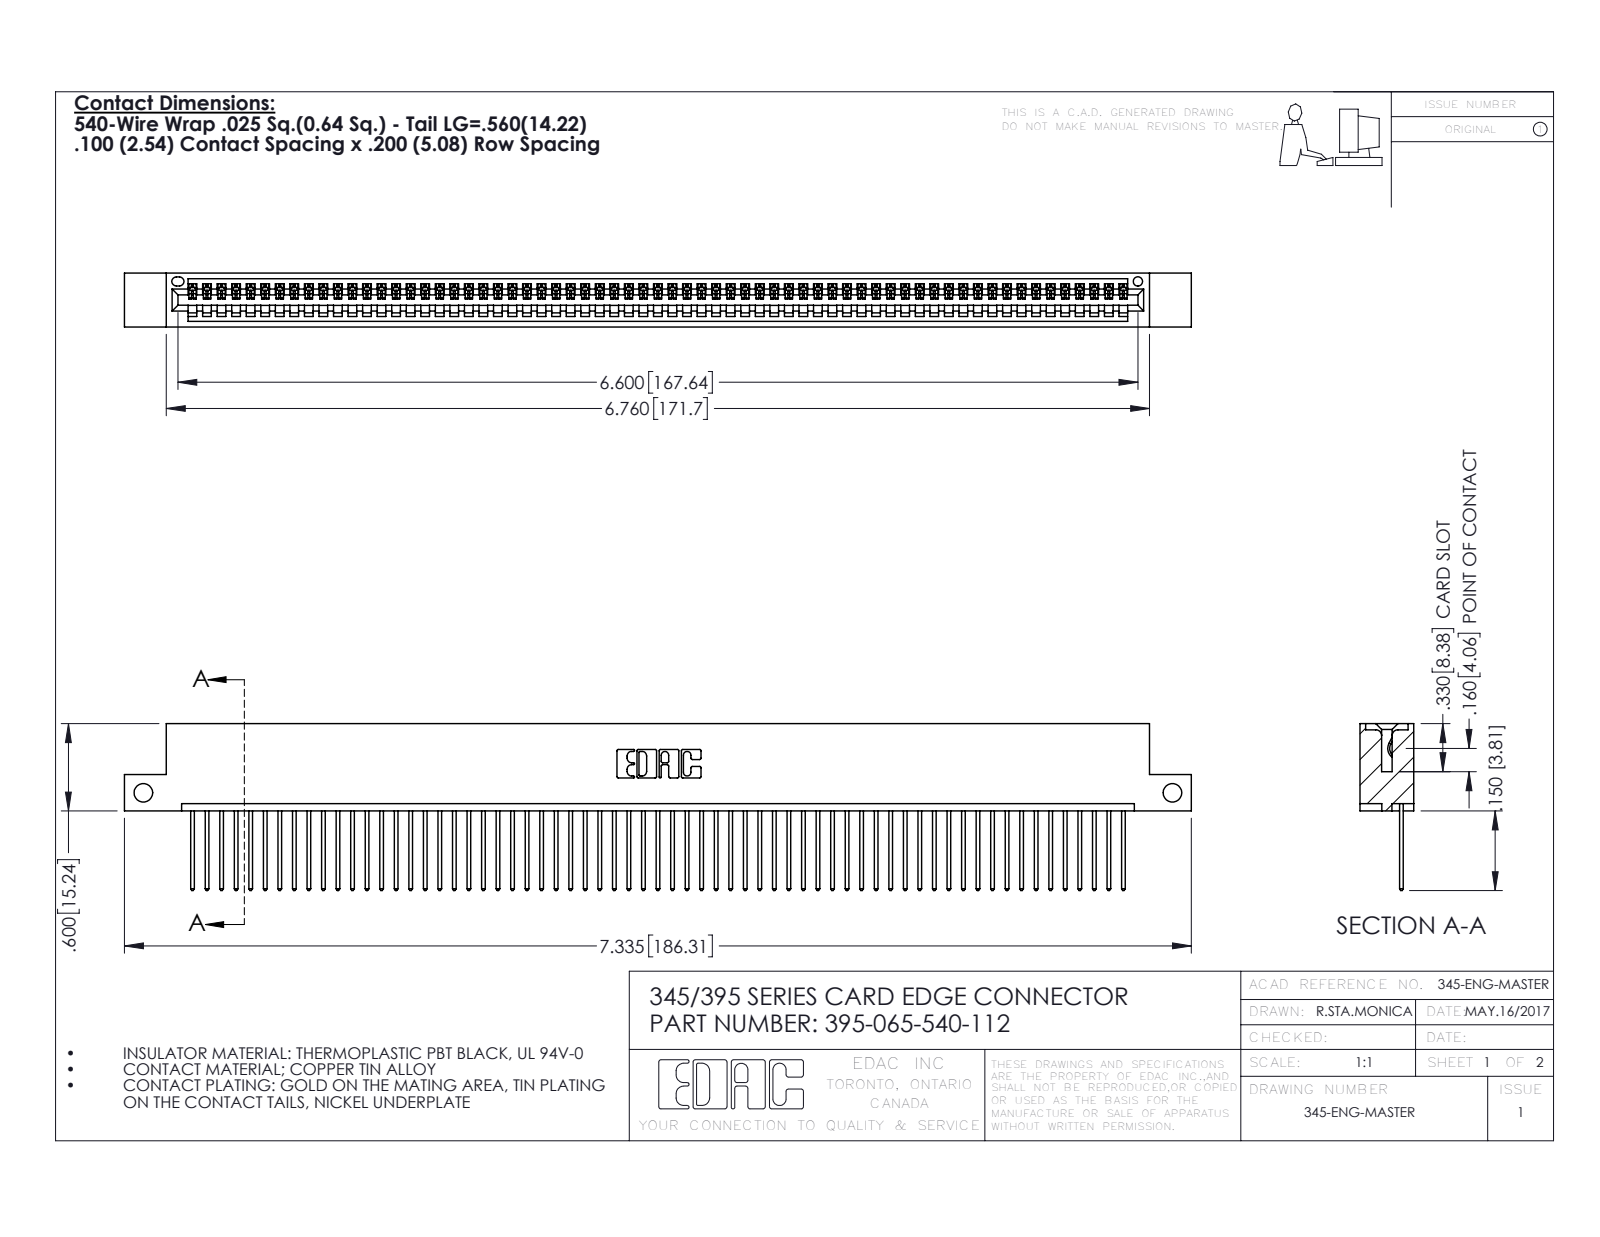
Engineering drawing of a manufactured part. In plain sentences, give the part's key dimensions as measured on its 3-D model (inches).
The part is named "395-065-540-112; 345-292-001_345-293-140; 345 Part_Flush Mounting Lugs - Side Mount". Its 3-D file was written by "SolidWorks 2016 (CONFIG_CONTROL_DESIGN)". It is 66 solids with 3896 faces: 2680 planar, 1216 cylindrical and 0 other. Overall it measures 7.335 by 1.147 by 0.37 inches. Its volume is 1.091 cubic inches and its surface area 38.09 square inches. Round holes: 2 of diameter 0.128, 1 of diameter 0.064. Partial cylindrical surfaces (rounded edges, fillets, slot ends): 130 of radius 0.006, 130 of radius 0.01, 22 of radius 0.01, 6 of radius 0.007, 6 of radius 0.031, 3 of radius 0.026, 2 of radius 0.031, 2 of radius 0.04. The main face-to-face distances are 0.072, 0.298, 0.37, 0.098, 0.272, 0.025, 0.2, 0.225, 0.149, 0.072. The hole center spacings are 7.075.
